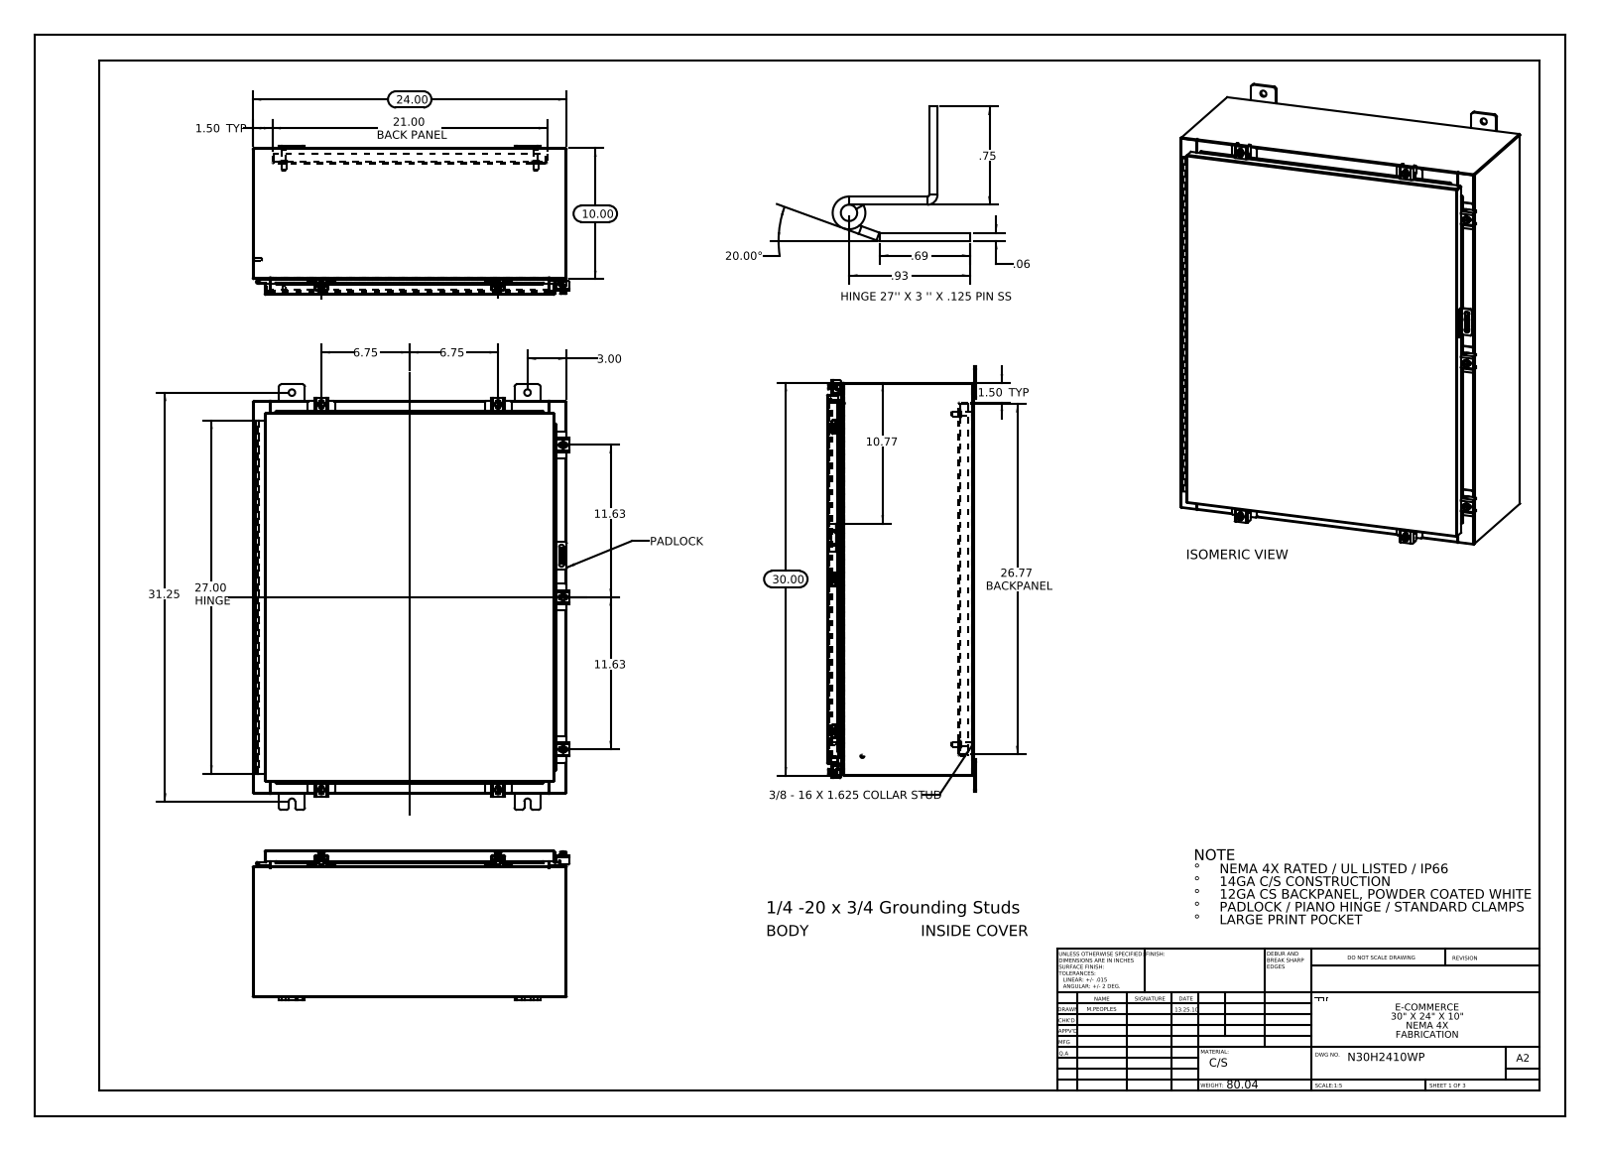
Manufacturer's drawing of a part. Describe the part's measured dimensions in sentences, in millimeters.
The part is named "N30H2410SSWP Cover; N30H2410SSWP Mounting Studs; N30H2410SSWP Bottom; N30H2410WP (+8 more)". Its 3-D file was written by "SolidWorks 2013 (CONFIG_CONTROL_DESIGN)". It is 54 solids with 2016 faces: 1062 planar, 838 cylindrical and 116 other. Overall it measures 825.5 by 615 by 289.3 millimeters. Its volume is 4 603 000 cubic millimeters and its surface area 4 549 000 square millimeters. Round holes: 8 of diameter 12.7, 7 of diameter 5.4, 7 of diameter 6.6, 2 of diameter 3.2. Round bosses or shafts: 8 of diameter 6.4, 7 of diameter 12.7, 7 of diameter 10.1, 4 of diameter 15.9, 4 of diameter 9.5, 4 of diameter 8.4, 2 of diameter 8, 2 of diameter 6. Partial cylindrical surfaces (rounded edges, fillets, slot ends): 34 of radius 1.5, 27 of radius 0.3, 24 of radius 4.8, 21 of radius 2.2, 14 of radius 3, 14 of radius 3.6, 11 of radius 1.3, 10 of radius 2. The main face-to-face distances are 1.9, 282.6, 280.7, 284.5, 2.6, 607.7, 25.4, 27.3, 255.3, 257.2. The hole center spacings are 698.5, 809.7, 47.2, 57.8, 59.1, 61.5, 90.4, 90.4.
